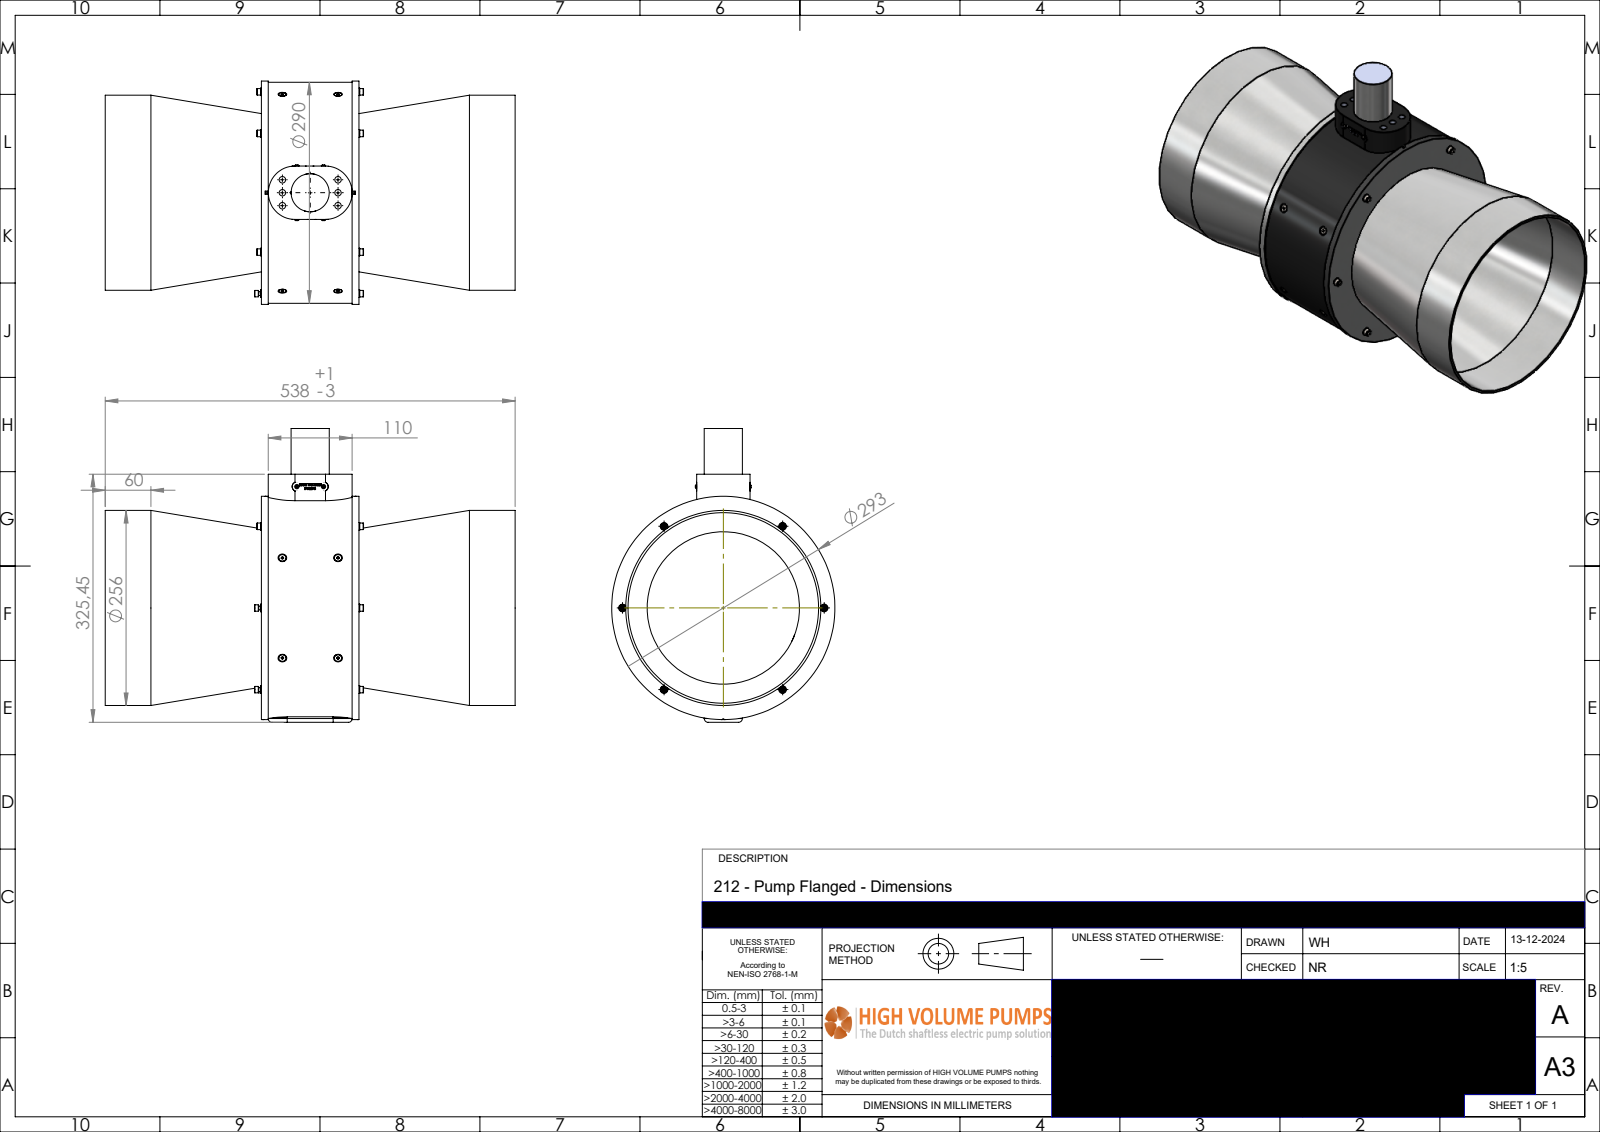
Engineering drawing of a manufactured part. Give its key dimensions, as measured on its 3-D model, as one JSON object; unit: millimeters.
{"part_name": "P-212-030-rev-A-PUF", "step_written_by": "SolidWorks 2024 (AUTOMOTIVE_DESIGN)", "units": "millimeters", "bodies": {"solids": 1, "faces": 1300, "planar": 726, "cylindrical": 266, "other": 308}, "overall_size": [538.06, 385.45, 293], "volume_mm3": 5454000, "surface_area_mm2": 936456, "round_holes": [[5.6, 6], [8.5, 6], [5.5, 4], [3.5, 2], [5.3, 2], [207, 1], [250, 1]], "round_bosses_or_shafts": [[5, 8], [10, 6], [9.64, 6], [8.5, 6], [5.7, 2], [293, 1], [290, 1], [256, 1]], "partial_cylinders_radius": [[5, 6], [10, 6], [2, 4], [3, 4], [15, 4], [25, 4], [1, 2], [6.15, 2]], "face_to_face_distances": [128.06, 205, 333.06, 5, 123.06, 210, 328.06, 325.45, 9, 4], "hole_center_spacings": [73, 17, 74.95, 132.37, 132.38, 264.75, 34, 80.53]}
